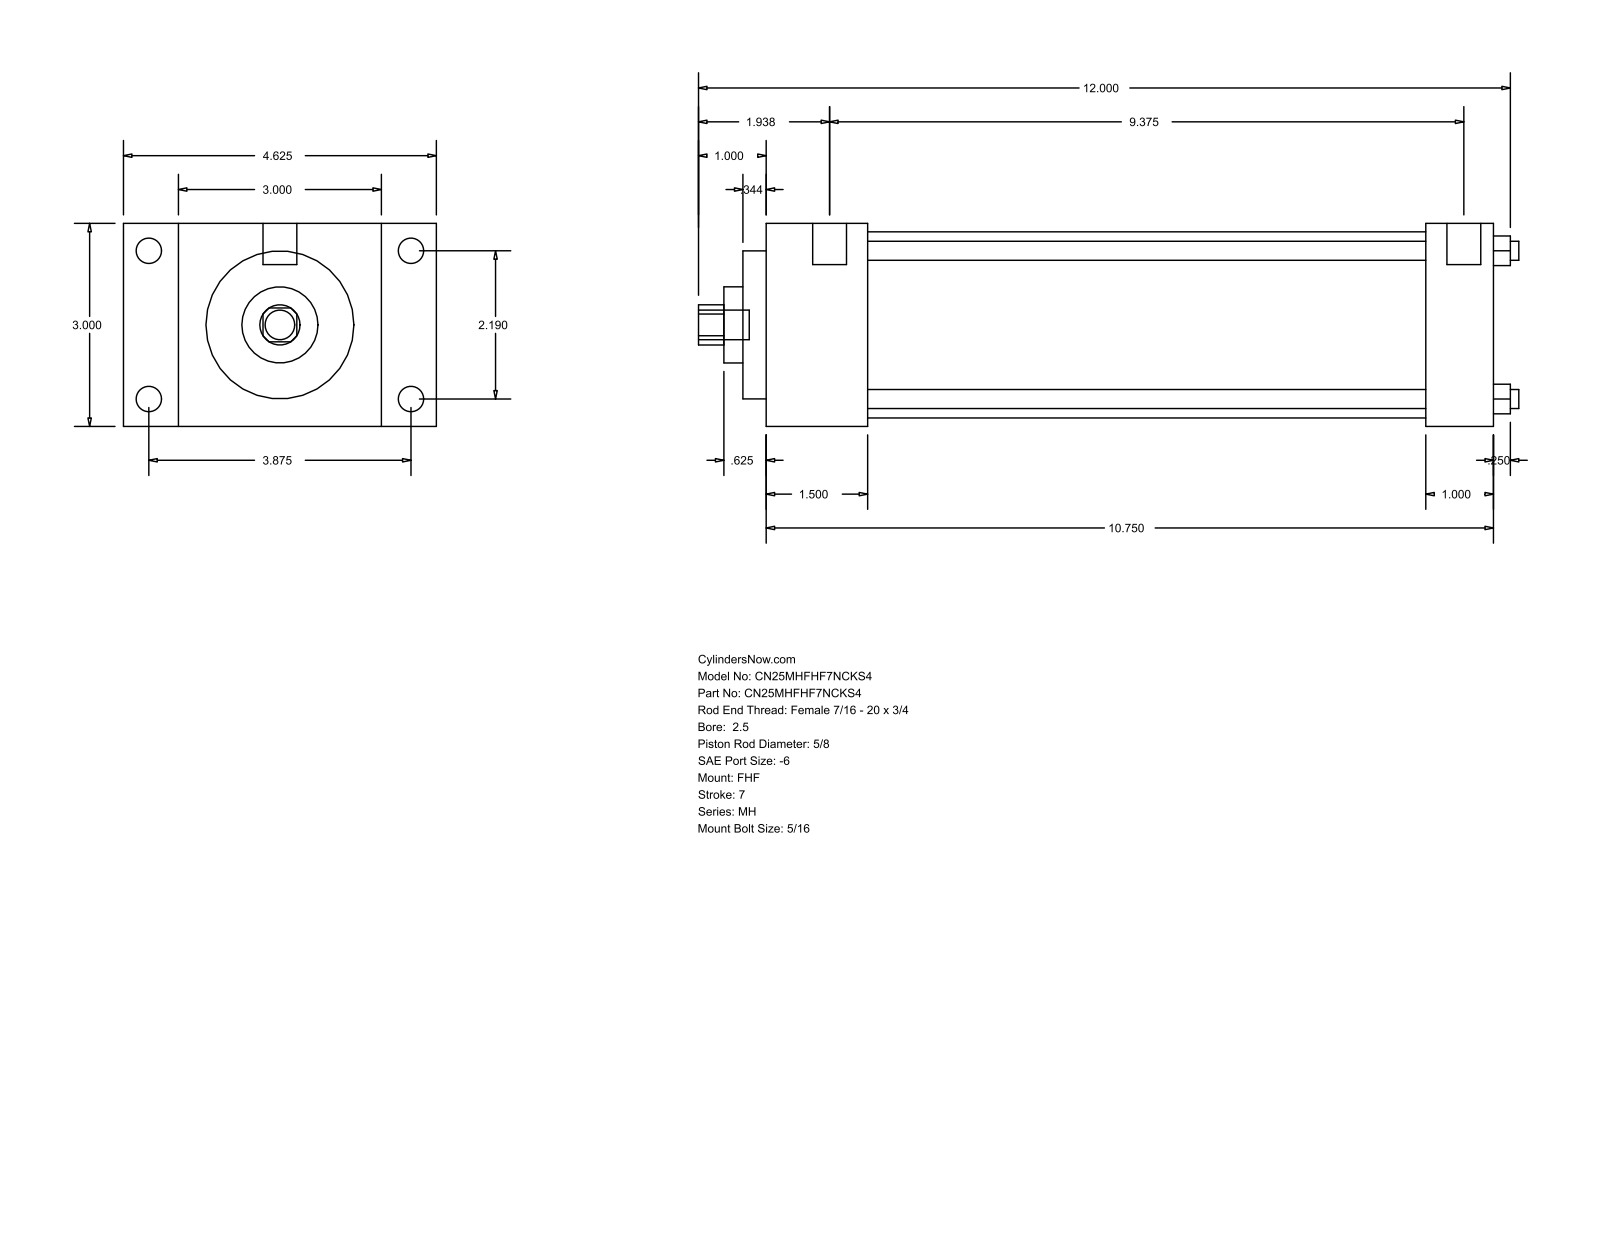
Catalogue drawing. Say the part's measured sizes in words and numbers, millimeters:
The part is named "MH_FHF__0250_0.625". Its 3-D file was written by "GSSL Pune (CONFIG_CONTROL_DESIGN)". It is 0 solids with 90 faces: 61 planar, 29 cylindrical and 0 other. Overall it measures 307.98 by 117.47 by 76.2 millimeters. Round holes: 4 of diameter 7.14, 1 of diameter 15.88, 1 of diameter 28.57, 1 of diameter 55.55, 1 of diameter 69.85. Round bosses or shafts: 4 of diameter 9.53, 4 of diameter 5.56, 2 of diameter 12.7, 1 of diameter 11.11. Partial cylindrical surfaces (rounded edges, fillets, slot ends): 1 of radius 7.54. The main face-to-face distances are 76.2, 273.05, 38.1, 234.95, 20.64, 96.84, 117.48, 25.4, 247.65, 209.55. The hole center spacings are 39.33, 55.62, 78.66.
